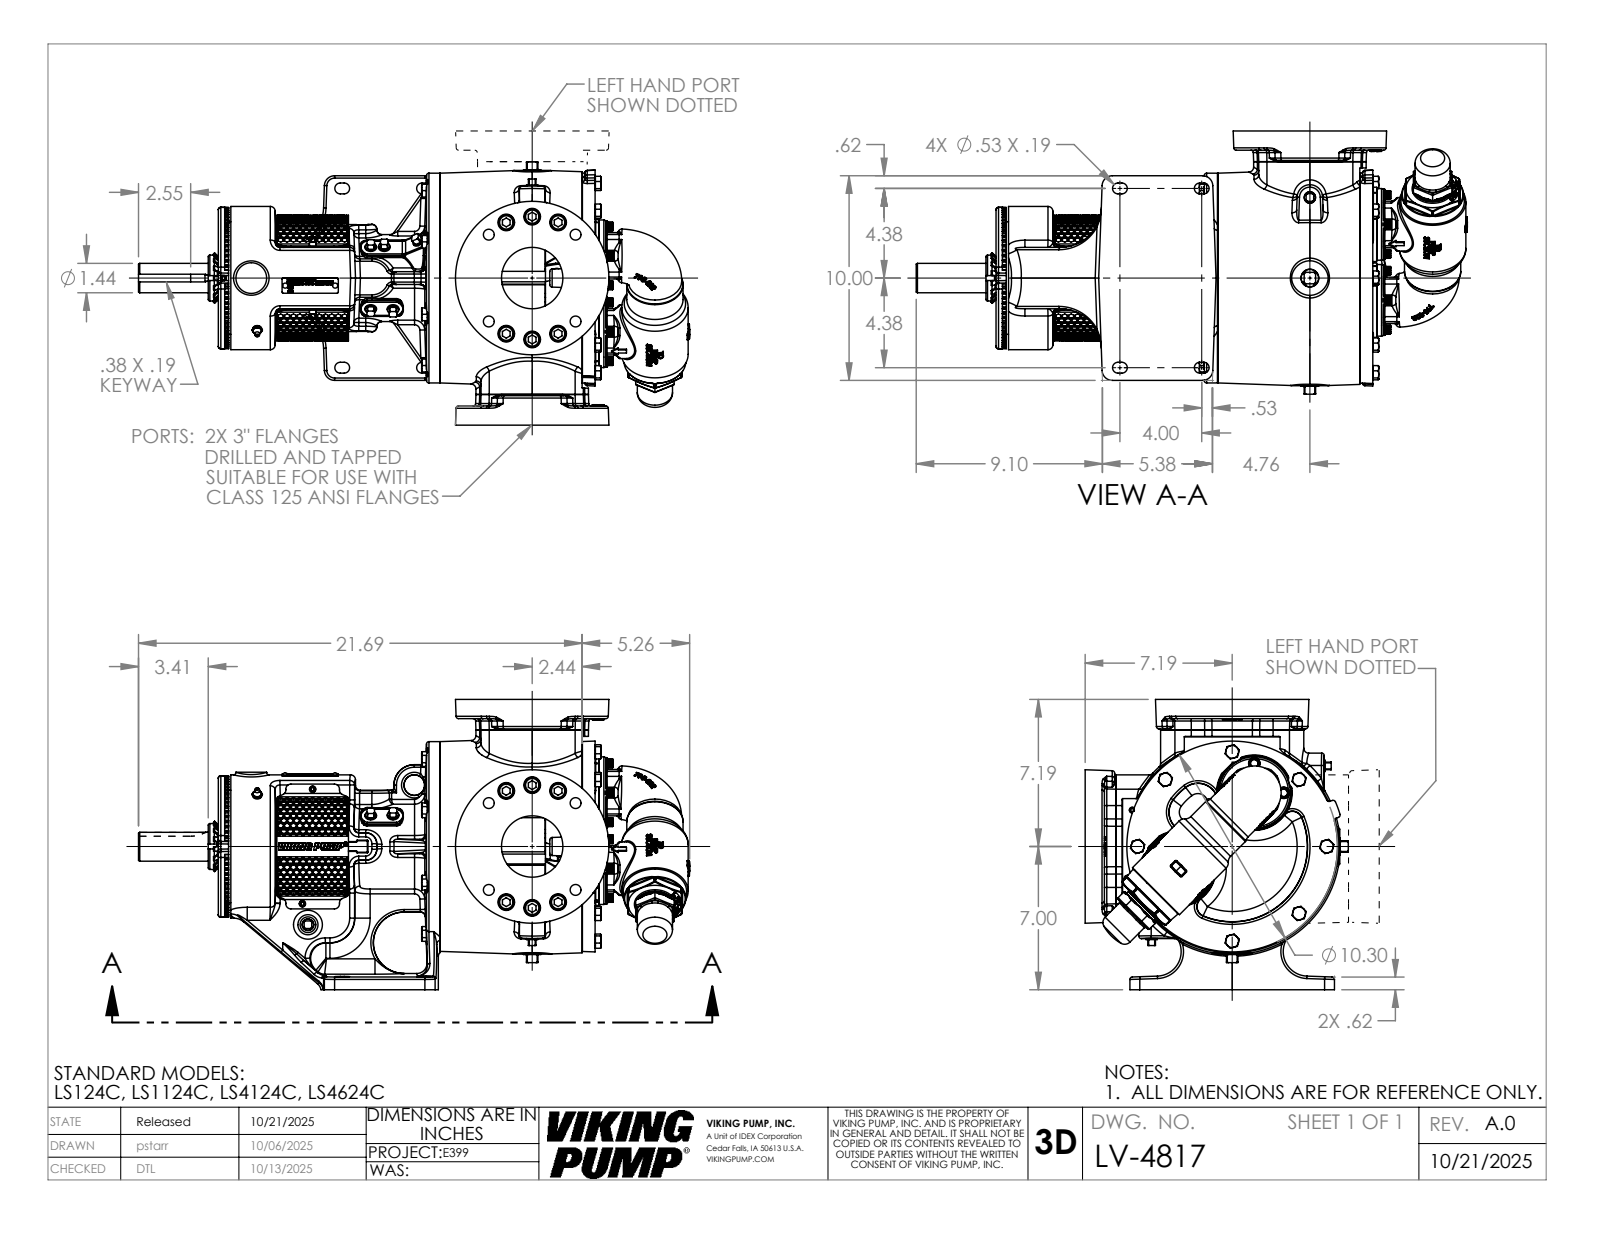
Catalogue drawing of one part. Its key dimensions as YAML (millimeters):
part_name: "LV-4817"
step_written_by: "SolidWorks 2024 (AUTOMOTIVE_DESIGN)"
units: millimeters
bodies: {solids: 1, faces: 6539, planar: 2042, cylindrical: 1218, other: 3279}
overall_size: [684.39, 360.36, 326.71]
volume: 19280000
surface_area: 989403
round_holes:
  - {diameter: 20.62, count: 12}
  - {diameter: 6.35, count: 9}
  - {diameter: 13.49, count: 8}
  - {diameter: 27.79, count: 8}
  - {diameter: 5.05, count: 6}
  - {diameter: 4.04, count: 3}
  - {diameter: 6.76, count: 2}
  - {diameter: 7.94, count: 2}
  - {diameter: 76.2, count: 2}
  - {diameter: 11.51, count: 1}
  - {diameter: 38.25, count: 1}
  - {diameter: 39.42, count: 1}
round_bosses_or_shafts:
  - {diameter: 19.05, count: 12}
  - {diameter: 15.88, count: 10}
  - {diameter: 14.29, count: 8}
  - {diameter: 15.87, count: 6}
  - {diameter: 88.9, count: 3}
  - {diameter: 7.92, count: 3}
  - {diameter: 4.83, count: 3}
  - {diameter: 260.35, count: 1}
partial_cylinders:
  - {radius: 1.61, count: 109}
  - {radius: 3.05, count: 82}
  - {radius: 1.75, count: 74}
  - {radius: 0.25, count: 56}
  - {radius: 6.1, count: 48}
  - {radius: 0.76, count: 38}
  - {radius: 11.43, count: 16}
  - {radius: 25.4, count: 16}
face_to_face_distances: [360.36, 12.7, 308.06, 89.94, 398, 57.15, 35.1, 54.33, 144.27, 452.33]
hole_center_spacings: [76.2, 107.76, 152.4, 34.93, 26.47, 32.98, 55.37, 58.32]
